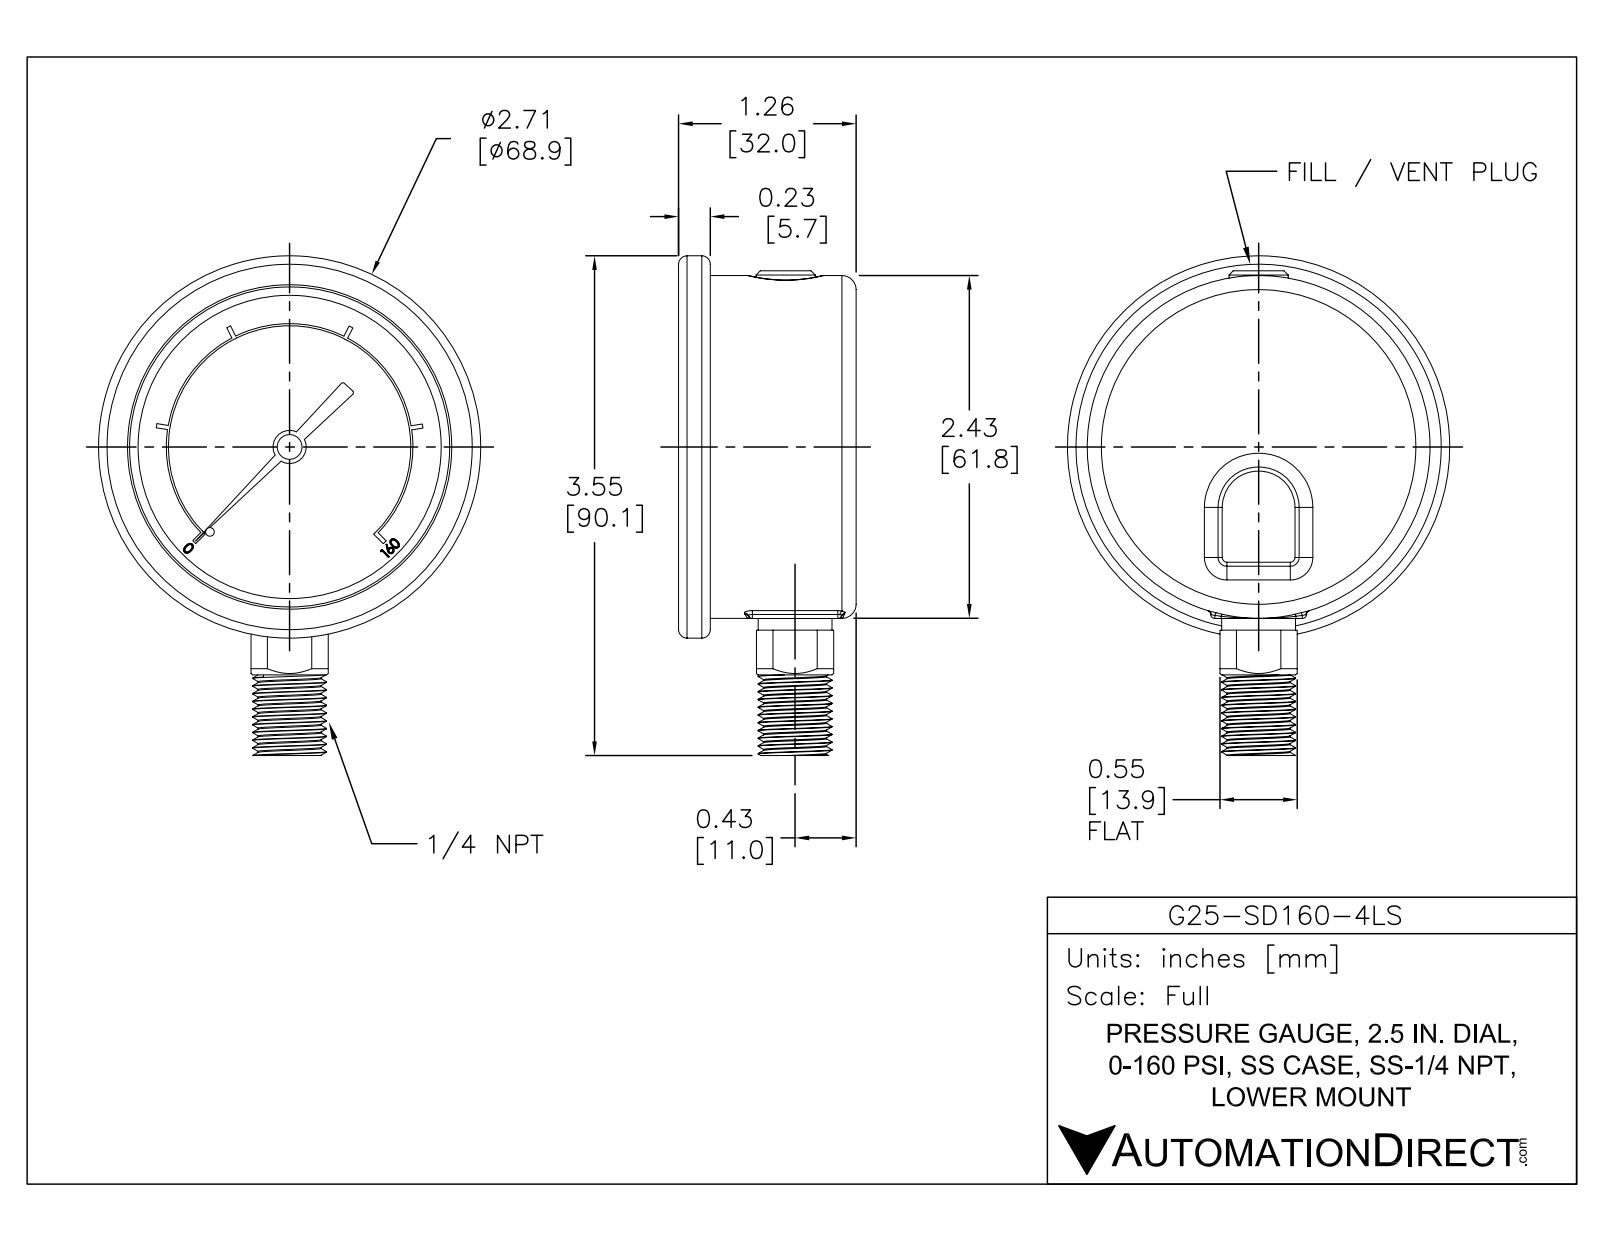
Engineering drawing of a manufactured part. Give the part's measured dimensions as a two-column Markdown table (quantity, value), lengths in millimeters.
| quantity | value |
| --- | --- |
| part name | G25-SD160-4LS |
| STEP written by | SolidWorks 2021 (AUTOMOTIVE_DESIGN) |
| units | millimeters |
| bodies | 1 solid, 346 faces (198 planar, 85 cylindrical, 63 other) |
| overall size | 90.1 × 68.9 × 32 |
| volume | 88 470 mm³ |
| surface area | 16 590 mm² |
| round holes (diameter × count) | 0.7 × 1, 1.8 × 1, 3 × 1, 57.7 × 1 |
| round bosses / shafts (diameter × count) | 68.9 × 1, 61.8 × 1, 13.3 × 1, 10.7 × 1, 6 × 1, 4.5 × 1, 3.6 × 1, 1 × 1 |
| partial cylindrical surfaces (radius × count) | 0.8 × 9, 2.5 × 3, 0.4 × 2, 8 × 1, 21.8 × 1, 22.2 × 1 |
| main face-to-face distances | 25.7, 32, 6.4, 26.3, 0.6, 5.7, 2.5, 23.1, 23.7, 29.5 |
| hole center spacings | 1.7 |
